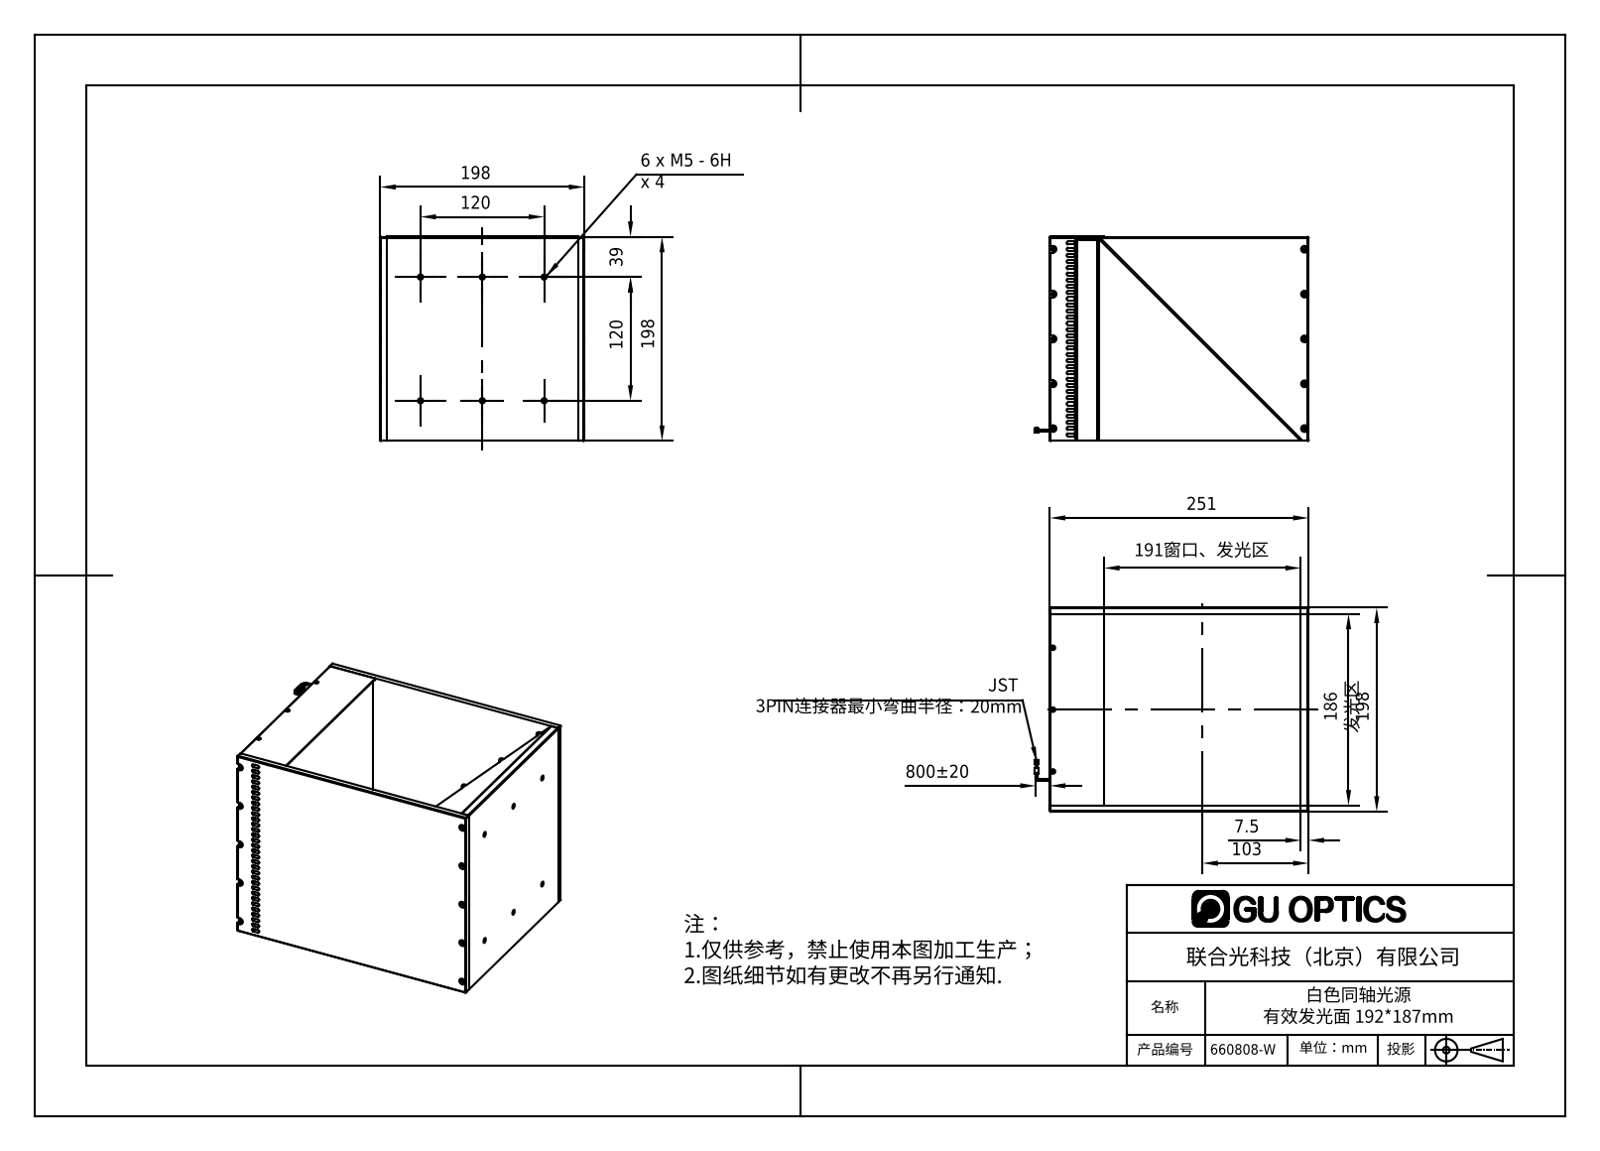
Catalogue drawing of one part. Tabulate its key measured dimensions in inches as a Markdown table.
| quantity | value |
| --- | --- |
| part name | 白色同轴光源 有效发光面 192187mm |
| STEP written by | SolidWorks 2016 (AUTOMOTIVE_DESIGN) |
| units | inches |
| bodies | 21 solids, 4677 faces (3722 planar, 818 cylindrical, 137 other) |
| overall size | 10.472 × 7.803 × 7.795 |
| volume | 82.02 in³ |
| surface area | 1 219 in² |
| round holes (diameter × count) | 0.098 × 26, 0.118 × 10, 0.134 × 10, 0.165 × 6, 0.197 × 6, 0.256 × 5, 0.276 × 5, 1.496 × 4, 1.89 × 4, 2.283 × 4, 0.063 × 3, 0.079 × 3 |
| round bosses / shafts (diameter × count) | 2.008 × 4, 1.614 × 4, 0.069 × 2 |
| partial cylindrical surfaces (radius × count) | 0.059 × 64, 0.069 × 32, 0.069 × 32, 0.07 × 32, 0.043 × 9, 0.02 × 8, 0.035 × 8, 0.041 × 8 |
| main face-to-face distances | 7.795, 7.559, 0.236, 0.079, 0.059, 7.717, 7.323, 8.091, 0.063, 8.012 |
| hole center spacings | 1.969, 1.392, 9.606, 2.784, 4.054, 3.425, 3.543, 3.937 |
